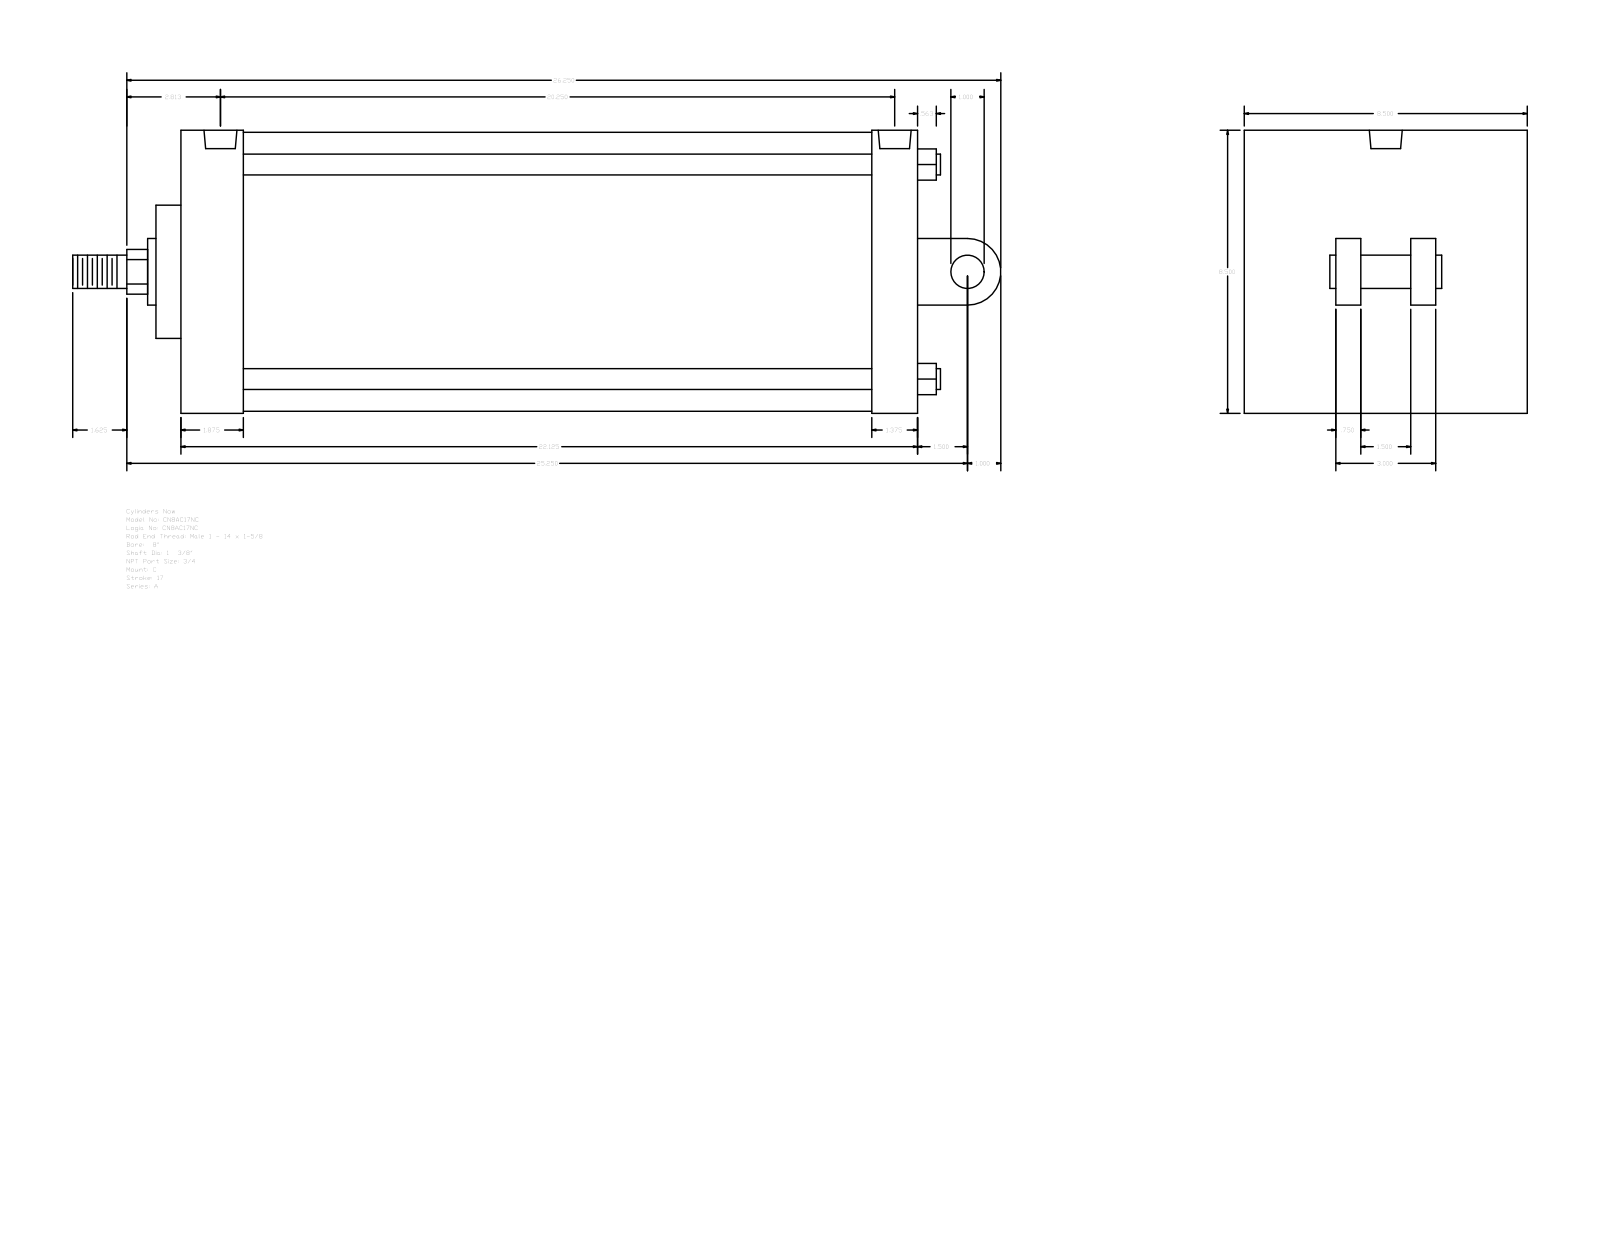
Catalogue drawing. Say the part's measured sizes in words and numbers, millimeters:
The part is named "A_C__0800_1.375". Its 3-D file was written by "GSSL Pune (CONFIG_CONTROL_DESIGN)". It is 0 solids with 104 faces: 75 planar, 29 cylindrical and 0 other. Overall it measures 708.02 by 215.9 by 215.9 millimeters. Round holes: 4 of diameter 15.08, 2 of diameter 25.12. Round bosses or shafts: 4 of diameter 15.88, 2 of diameter 25.4, 1 of diameter 212.72, 1 of diameter 50.8, 1 of diameter 34.92. Partial cylindrical surfaces (rounded edges, fillets, slot ends): 1 of radius 17.06, 1 of radius 25.4. The main face-to-face distances are 561.98, 215.9, 57.15, 47.63, 514.35, 527.06, 479.43, 34.92, 88.9, 69.85. The hole center spacings are 6.35, 501.65, 508, 514.35.
